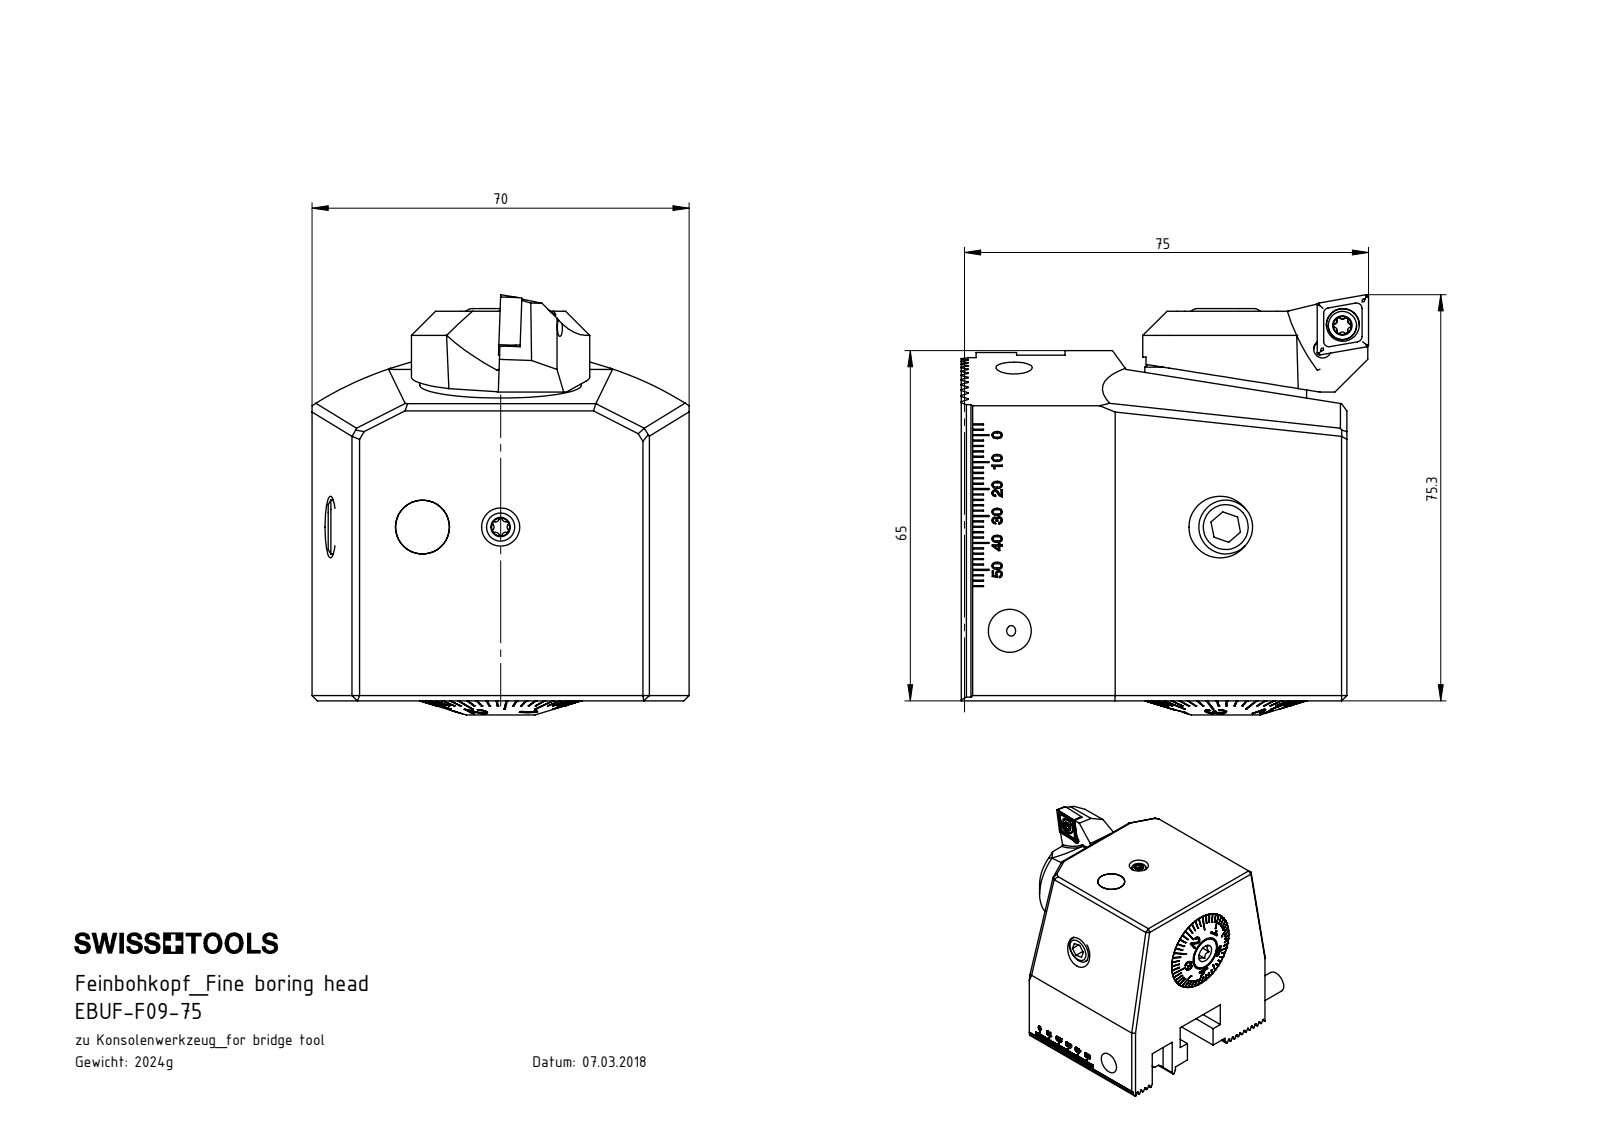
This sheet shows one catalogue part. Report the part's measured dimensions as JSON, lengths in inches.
{"part_name": "F72-BG1.011.056_D; VK1-F0U.001.075_C; F72-BG2.014.020_B; A55-BG2.011.016_D (+8 more)", "step_written_by": "SolidWorks 2017 (CONFIG_CONTROL_DESIGN)", "units": "inches", "bodies": {"solids": 20, "faces": 1222, "planar": 640, "cylindrical": 187, "other": 395}, "overall_size": [3.228, 3.069, 2.976], "volume_in3": 15.76, "surface_area_in2": 95.13, "round_holes": [[0.13, 4], [0.315, 3], [0.335, 2], [0.165, 1], [0.173, 1], [0.197, 1], [0.24, 1], [0.268, 1], [0.394, 1], [0.433, 1], [0.463, 1], [0.472, 1]], "round_bosses_or_shafts": [[0.394, 2], [0.207, 2], [0.157, 2], [1.18, 1], [1.177, 1], [0.984, 1], [0.709, 1], [0.63, 1]], "partial_cylinders_radius": [[0.006, 22], [0.013, 12], [0.023, 12], [0.02, 4], [0.126, 3], [0.394, 2], [0.039, 1], [0.065, 1]], "face_to_face_distances": [0.068, 0.205, 0.341, 2.756, 0.273, 0.136, 2.06, 1.705, 0.965, 1.791], "hole_center_spacings": [0.225, 0.231, 0.276, 0.571, 1.735, 1.75, 1.886]}
